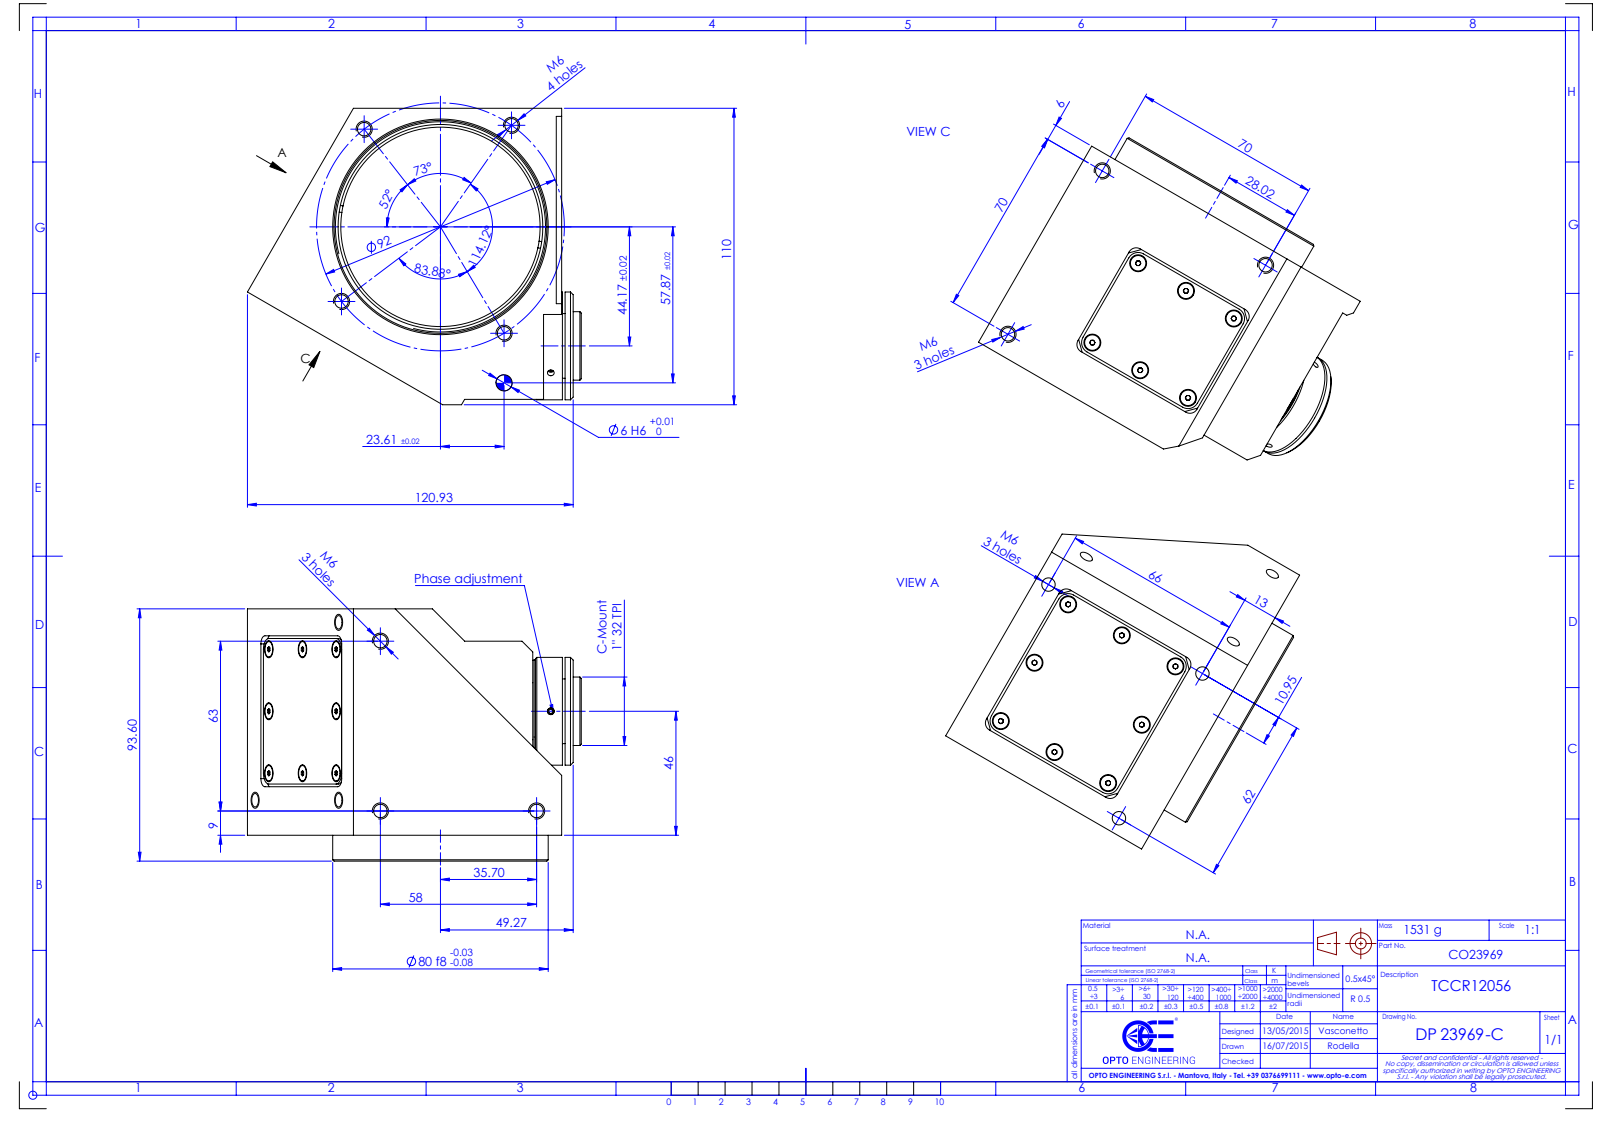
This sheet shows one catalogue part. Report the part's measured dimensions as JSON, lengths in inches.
{"part_name": "DP23969_TCCR12056", "step_written_by": "SolidWorks 2021 (CONFIG_CONTROL_DESIGN)", "units": "inches", "bodies": {"solids": 0, "faces": 412, "planar": 204, "cylindrical": 116, "other": 92}, "overall_size": [4.879, 4.331, 3.685], "round_holes": [[0.197, 13], [0.098, 3], [0.071, 2], [0.236, 1], [0.571, 1], [0.866, 1], [0.886, 1], [2.913, 1], [2.992, 1]], "round_bosses_or_shafts": [[0.226, 19], [3.15, 1], [1.575, 1], [1.504, 1], [1.488, 1], [1, 1]], "partial_cylinders_radius": [[0.157, 10], [0.118, 8]], "face_to_face_distances": [3.307, 0.02, 0.02, 0.079, 4.252, 0.472, 0.039, 0.422, 2.854, 1.398], "hole_center_spacings": [1.811, 0.394, 2.756, 0.724, 0.787, 1.471, 2.154, 2.283]}
